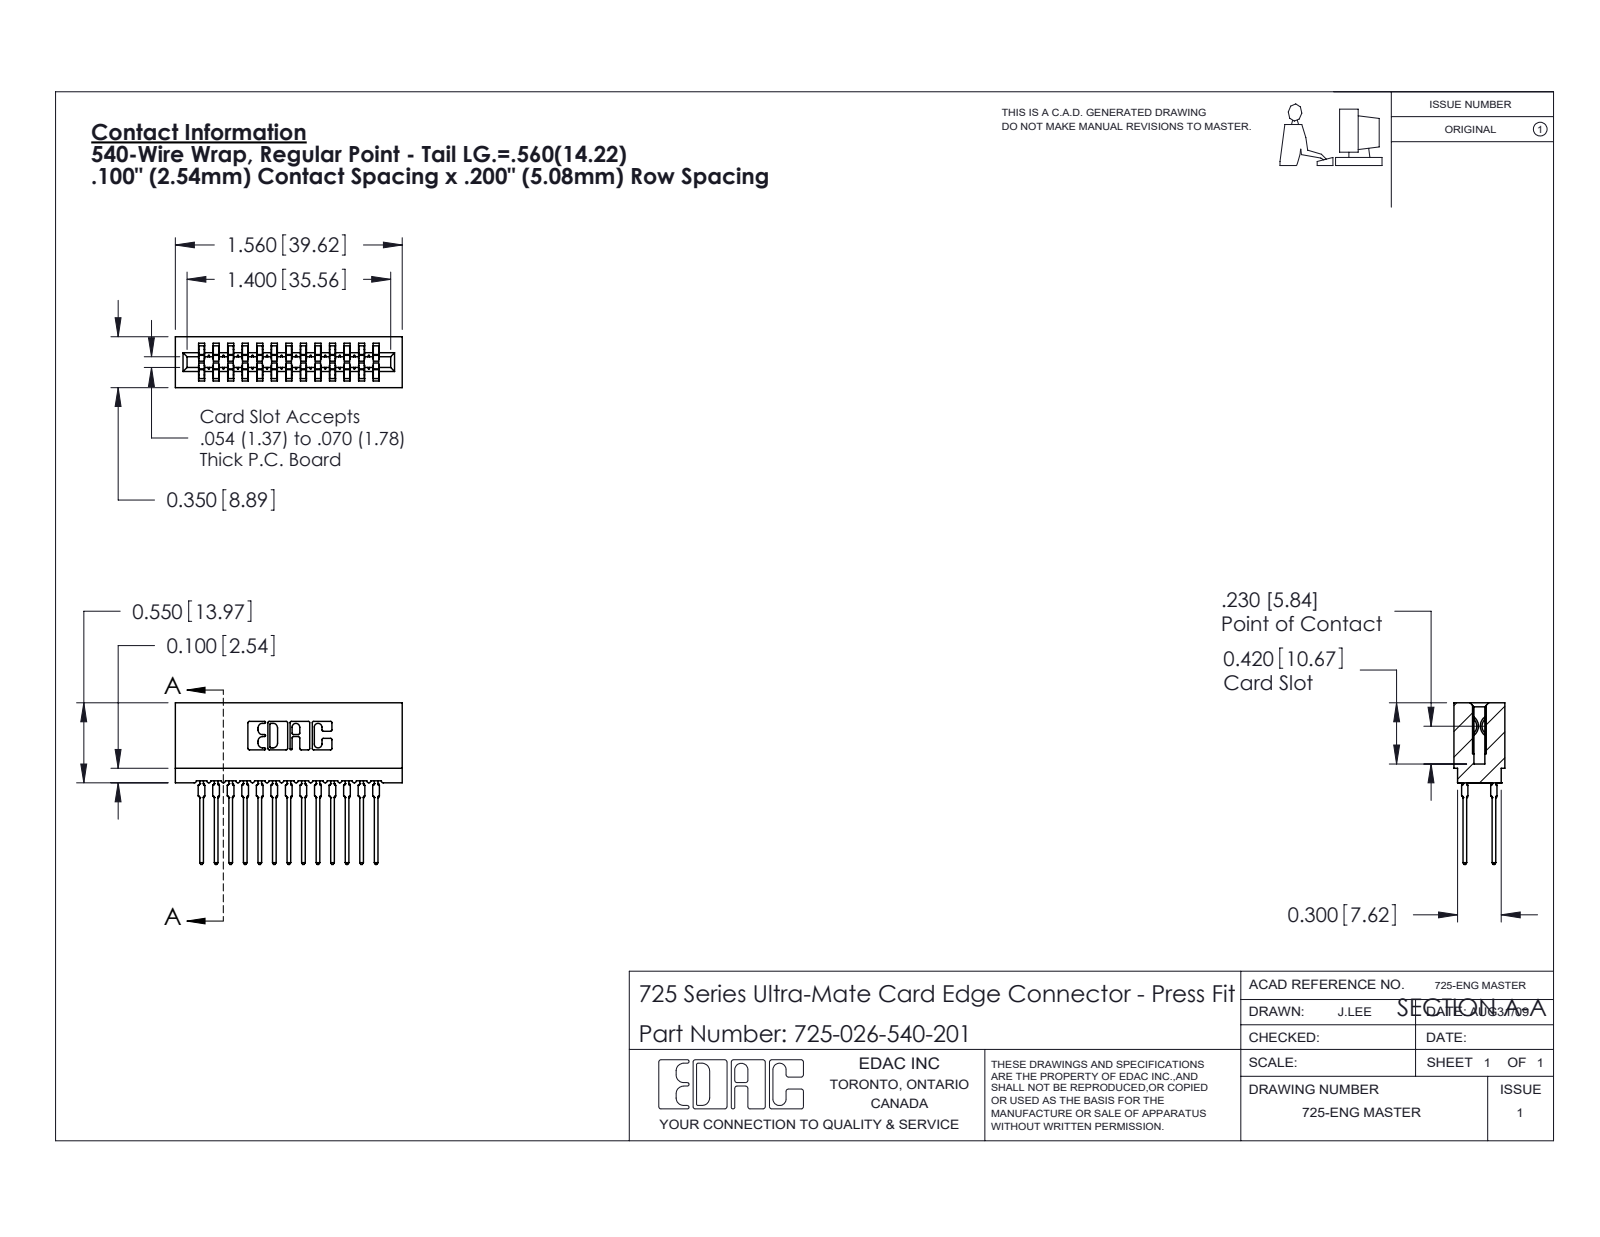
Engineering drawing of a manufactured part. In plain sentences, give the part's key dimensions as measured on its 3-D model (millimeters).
The part is named "725 Part_Insulator Option - 01; 745-292-001_540; 725-026-540-201". Its 3-D file was written by "SolidWorks 2020 (CONFIG_CONTROL_DESIGN)". It is 27 solids with 2422 faces: 1251 planar, 495 cylindrical and 676 other. Overall it measures 39.6 by 28.2 by 8.9 millimeters. Its volume is 3 360 cubic millimeters and its surface area 6 787 square millimeters. Partial cylindrical surfaces (rounded edges, fillets, slot ends): 52 of radius 0.5, 26 of radius 0.4, 22 of radius 0.3, 8 of radius 0.1, 8 of radius 0.3, 6 of radius 0.2, 6 of radius 0.8, 3 of radius 0.7. The main face-to-face distances are 5.1, 2.5, 7.6, 10.2, 12.7, 1.6, 7.3, 15.2, 8.9, 5.4.
